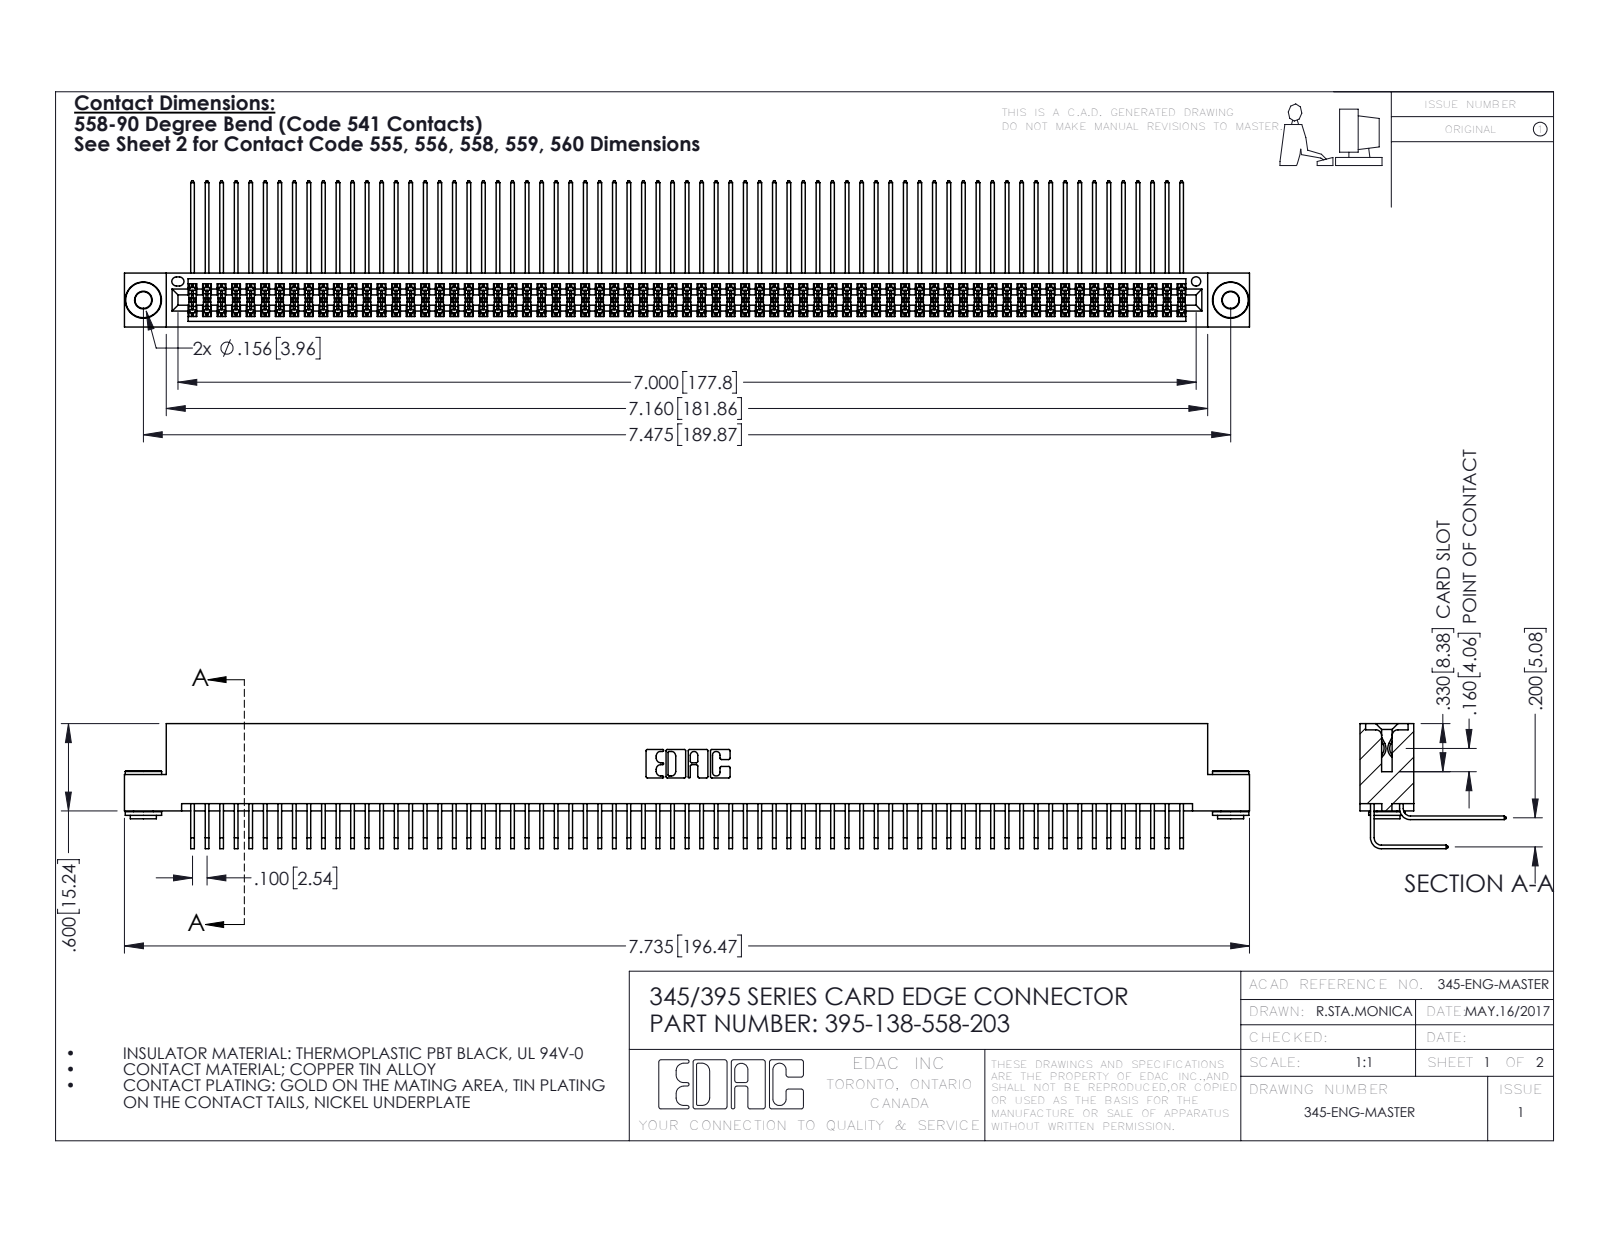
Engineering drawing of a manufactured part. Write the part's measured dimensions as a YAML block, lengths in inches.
part_name: "395-138-558-203; 345 Part_Flush Mounting Lugs - 0.156 Dia-TH; 345-292-001_558 Tail - 2; 345-250-002_345-250-002-102 (+1 more)"
step_written_by: "SolidWorks 2016 (CONFIG_CONTROL_DESIGN)"
units: inches
bodies: {solids: 141, faces: 7340, planar: 4920, cylindrical: 2412, other: 8}
overall_size: [7.735, 1.005, 0.859]
volume: 1.23
surface_area: 53.1
round_holes:
  - {diameter: 0.116, count: 2}
  - {diameter: 0.156, count: 2}
  - {diameter: 0.064, count: 1}
round_bosses_or_shafts:
  - {diameter: 0.25, count: 2}
  - {diameter: 0.18, count: 2}
  - {diameter: 0.136, count: 2}
partial_cylinders:
  - {radius: 0.006, count: 275}
  - {radius: 0.01, count: 22}
  - {radius: 0.007, count: 6}
  - {radius: 0.031, count: 6}
  - {radius: 0.026, count: 3}
  - {radius: 0.014, count: 2}
  - {radius: 0.019, count: 2}
  - {radius: 0.022, count: 2}
face_to_face_distances: [0.072, 0.298, 0.2, 0.37, 0.025, 0.098, 0.272, 0.225, 0.025, 0.175]
hole_center_spacings: [0.27, 7.239, 7.475]
